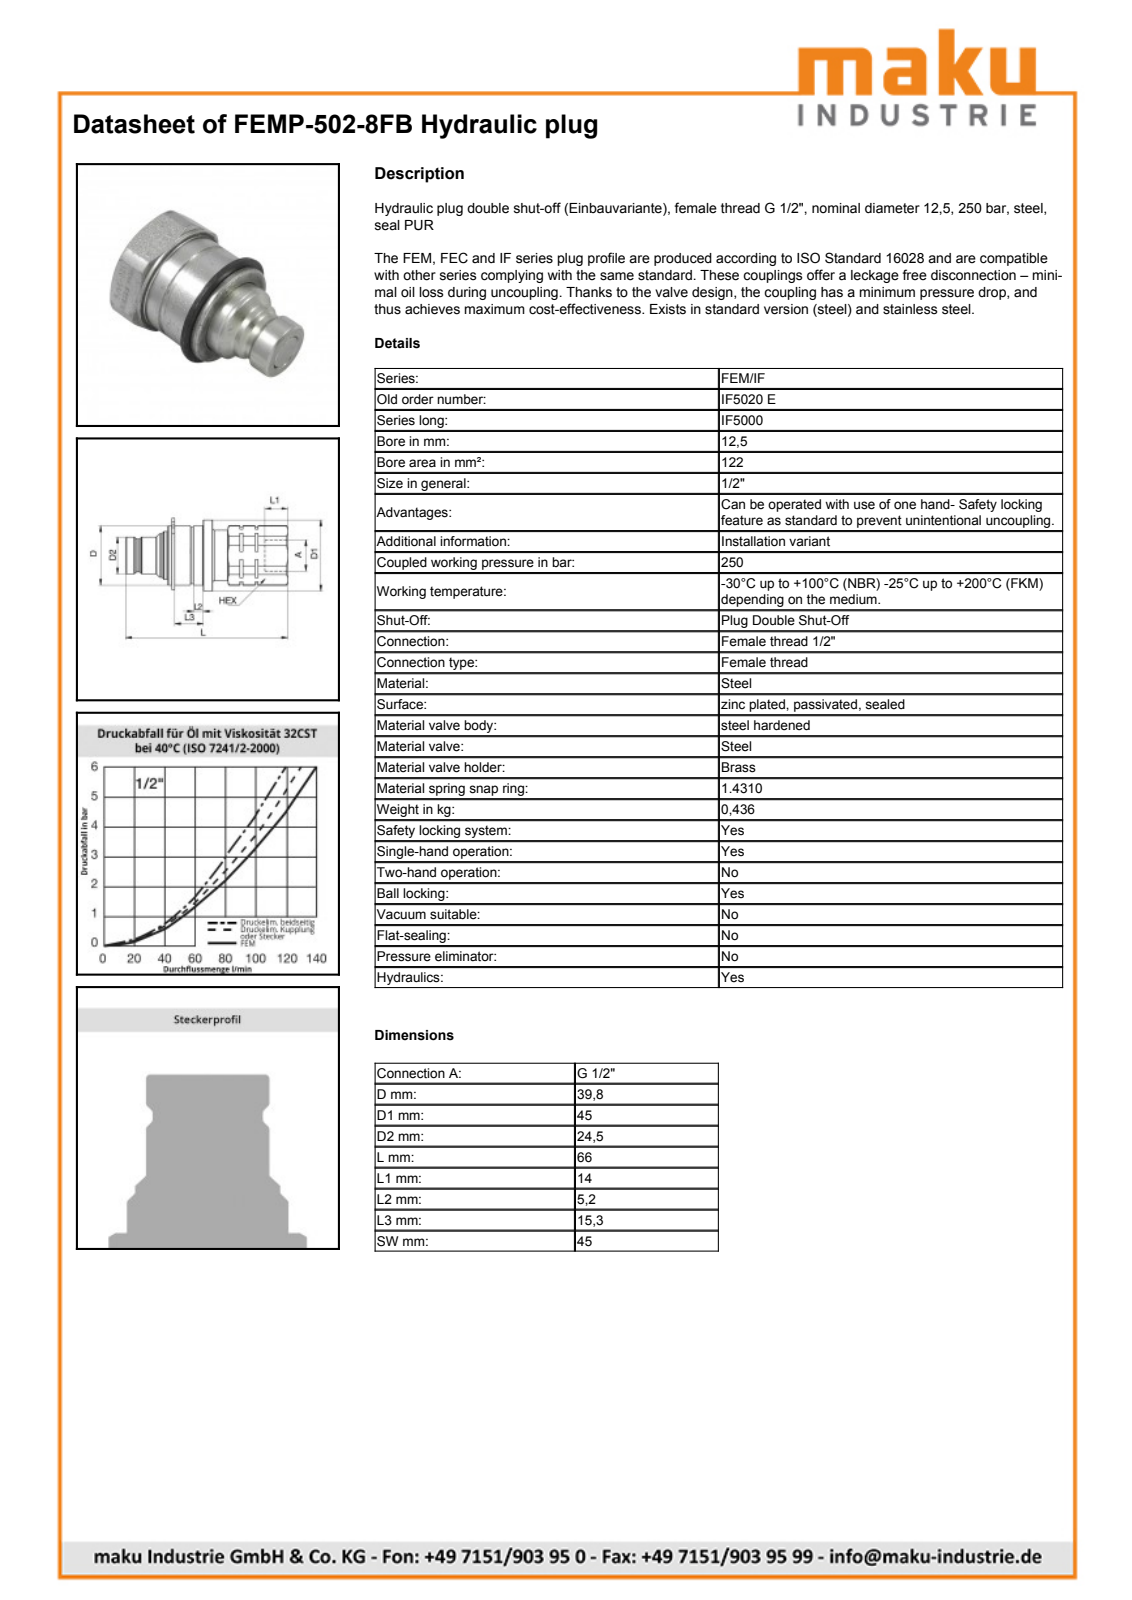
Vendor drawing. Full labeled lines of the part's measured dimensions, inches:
Part name (STEP PRODUCT): FEMP-502-8FB
STEP written by: SolidWorks 2009 (AUTOMOTIVE_DESIGN)
Units: inches
Bodies: 1 solid, 123 faces (26 planar, 48 cylindrical, 49 other)
Overall size (bounding box): 2.602 × 1.969 × 1.772
Volume: 4.338 in³ · Surface area: 20.73 in²
Round holes (diameter × count): ⌀0.098 ×2, ⌀0.618 ×1, ⌀0.733 ×1, ⌀1.228 ×1
Round bosses / shafts (diameter × count): ⌀1.764 ×1, ⌀1.567 ×1, ⌀1.476 ×1, ⌀1.22 ×1, ⌀1.201 ×1, ⌀0.965 ×1, ⌀0.866 ×1, ⌀0.612 ×1
Partial cylindrical surfaces — rounded edges, fillets, slot ends (radius × count): R0.118 ×2, R0.276 ×2, R0.856 ×1, R0.954 ×1, R0.984 ×1
Main face-to-face distances: 1.772, 1.518, 0.142, 1.659, 0.073, 0.069, 1.587, 1.026, 0.953, 0.884
Hole centre spacings: 0.818, 0.394
